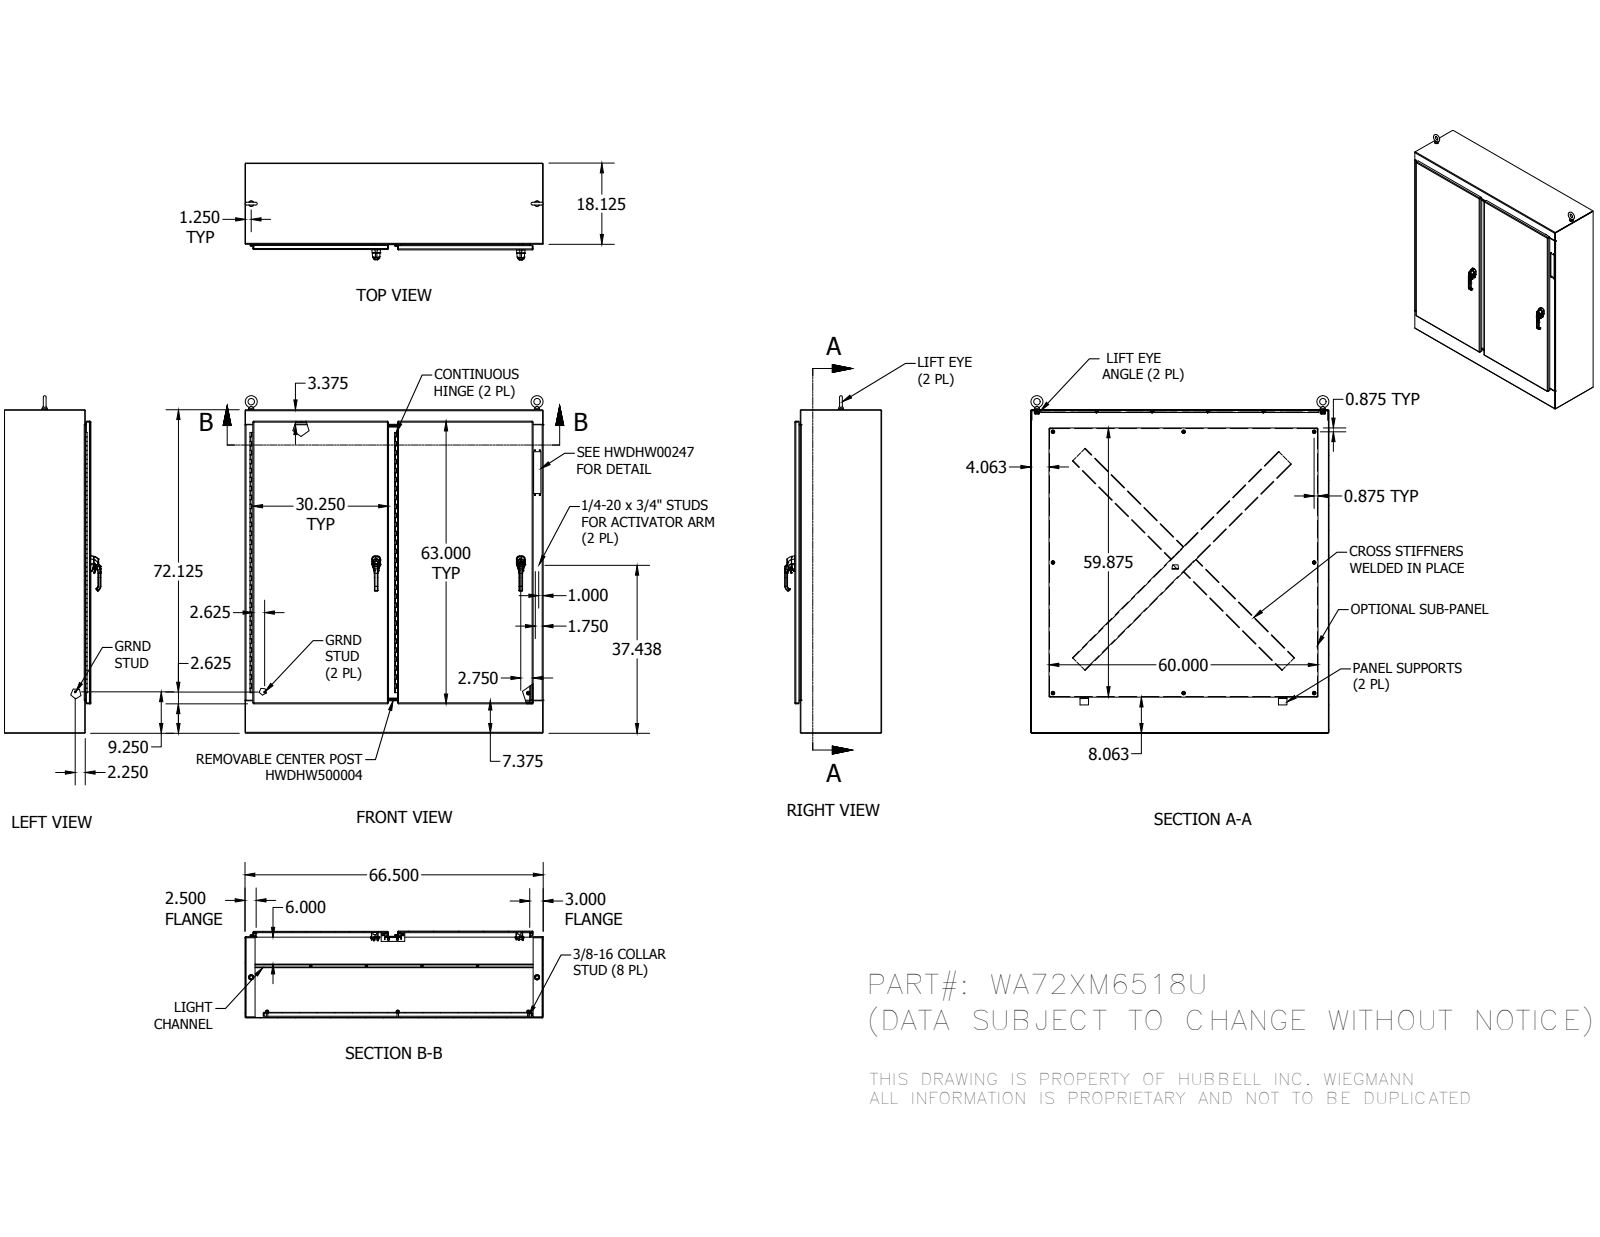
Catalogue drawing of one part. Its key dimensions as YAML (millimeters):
part_name: "WA72XM65U_BACK; 3889; 349104; HFW3878 (+8 more)"
step_written_by: "Autodesk Inventor 2014 (AUTOMOTIVE_DESIGN)"
units: millimeters
bodies: {solids: 226, faces: 8874, planar: 4148, cylindrical: 2898, other: 1828}
overall_size: [1911.29, 1689.1, 548.73]
volume: 35250000
surface_area: 22830000
round_holes:
  - {diameter: 6.35, count: 18}
  - {diameter: 9.52, count: 18}
  - {diameter: 7.02, count: 16}
  - {diameter: 7.14, count: 10}
  - {diameter: 4.83, count: 8}
  - {diameter: 5.08, count: 8}
  - {diameter: 7.33, count: 8}
  - {diameter: 7.8, count: 8}
  - {diameter: 7.94, count: 8}
  - {diameter: 8.51, count: 8}
  - {diameter: 9.65, count: 8}
  - {diameter: 4.98, count: 7}
round_bosses_or_shafts:
  - {diameter: 8.38, count: 18}
  - {diameter: 6.35, count: 18}
  - {diameter: 15.88, count: 13}
  - {diameter: 9.52, count: 12}
  - {diameter: 8.56, count: 12}
  - {diameter: 14.29, count: 9}
  - {diameter: 7.11, count: 8}
  - {diameter: 25.4, count: 7}
partial_cylinders:
  - {radius: 0.5, count: 366}
  - {radius: 0.3, count: 216}
  - {radius: 0.51, count: 192}
  - {radius: 0.47, count: 44}
  - {radius: 1.27, count: 32}
  - {radius: 2, count: 28}
  - {radius: 1.59, count: 24}
  - {radius: 1.5, count: 23}
face_to_face_distances: [3.17, 3.18, 1.59, 31.23, 29.64, 4.77, 488.43, 485.26, 486.84, 483.67]
hole_center_spacings: [1371.28, 1390.33, 1479.55, 1.59, 1380.81, 1390.34, 1399.85, 9.66]
